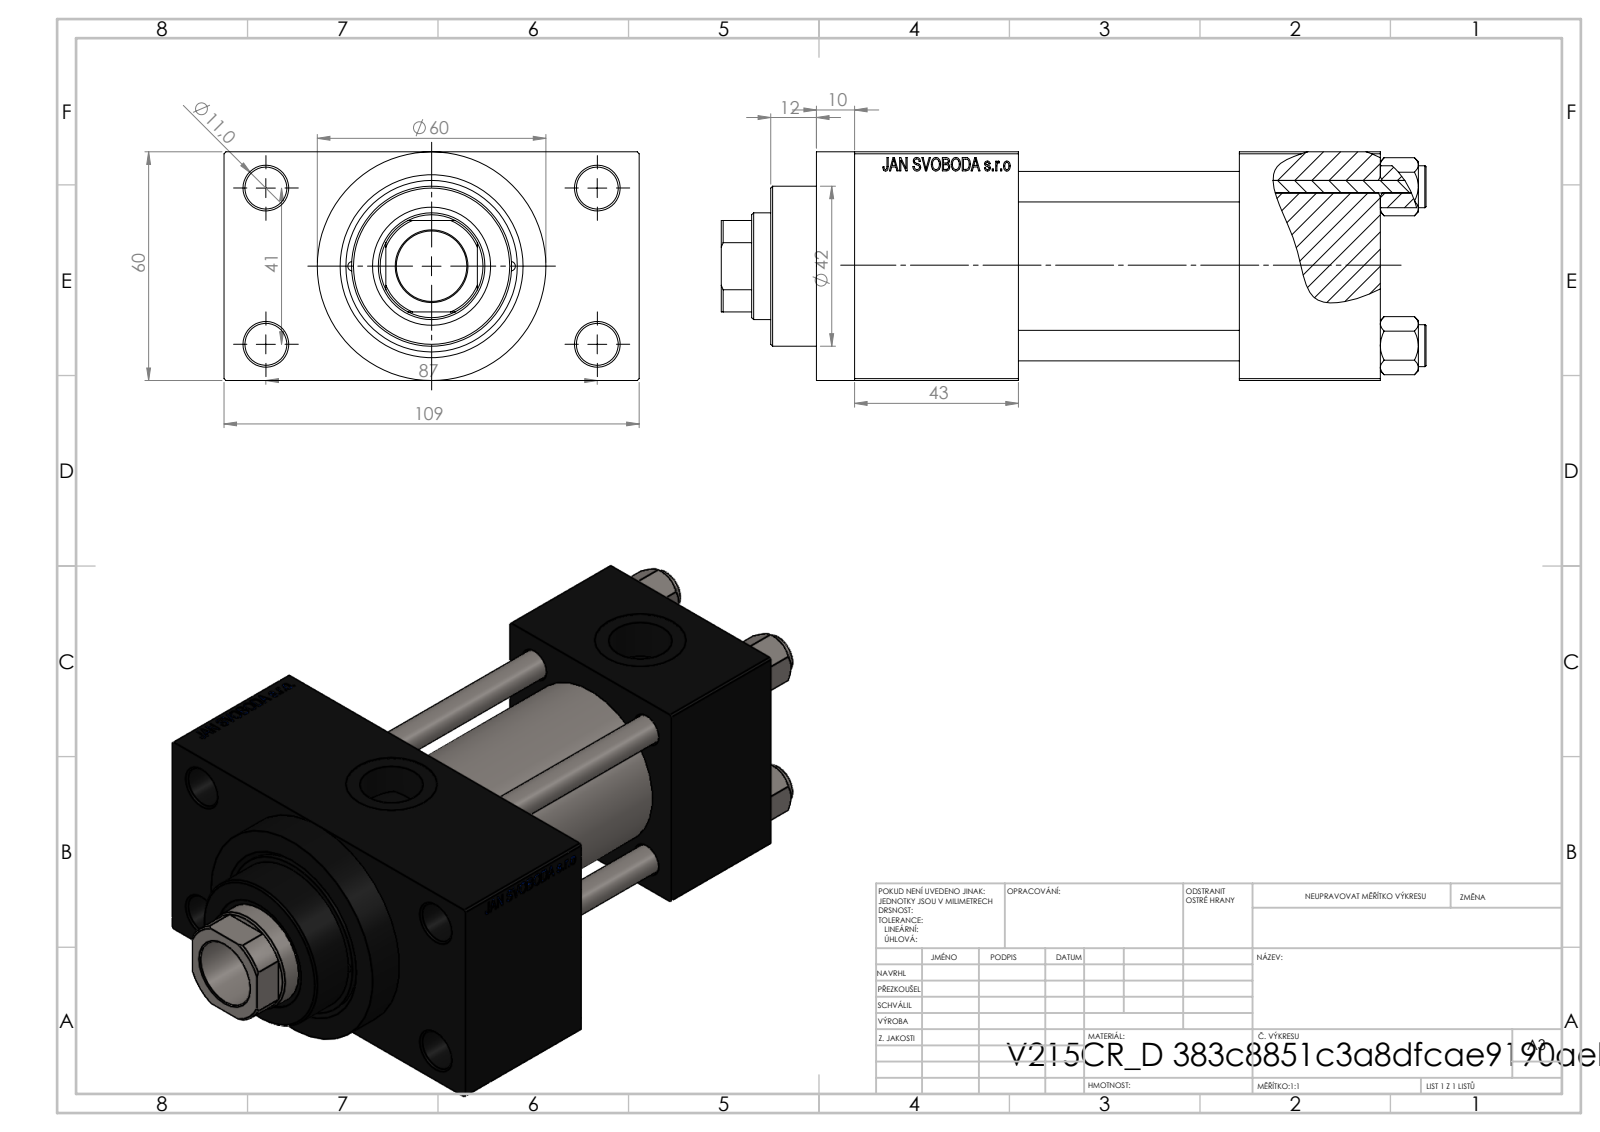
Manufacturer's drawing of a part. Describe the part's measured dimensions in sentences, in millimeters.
The part is named "NUT_M5_D; V215CR_D_TYCINKA; V215CR_VCP_D; V215CR_D_Body (+1 more)". Its 3-D file was written by "SolidWorks 2019 (CONFIG_CONTROL_DESIGN)". It is 11 solids with 1115 faces: 502 planar, 93 cylindrical and 520 other. Overall it measures 185 by 109 by 60 millimeters. Its volume is 533 909 cubic millimeters and its surface area 127 796 square millimeters. Round holes: 4 of diameter 8, 4 of diameter 11, 2 of diameter 2.5, 2 of diameter 7, 2 of diameter 16.66, 2 of diameter 24, 1 of diameter 18.5, 1 of diameter 28, 1 of diameter 31, 1 of diameter 40, 1 of diameter 45. Round bosses or shafts: 4 of diameter 11, 1 of diameter 60, 1 of diameter 46, 1 of diameter 42. Partial cylindrical surfaces (rounded edges, fillets, slot ends): 1 of radius 13.5. The main face-to-face distances are 60, 84.5, 24.5, 58, 37, 95, 138, 101, 43, 109. The hole center spacings are 20.85, 22.65, 29.49, 30.62, 41.7, 46.53, 47.15, 48.09.
